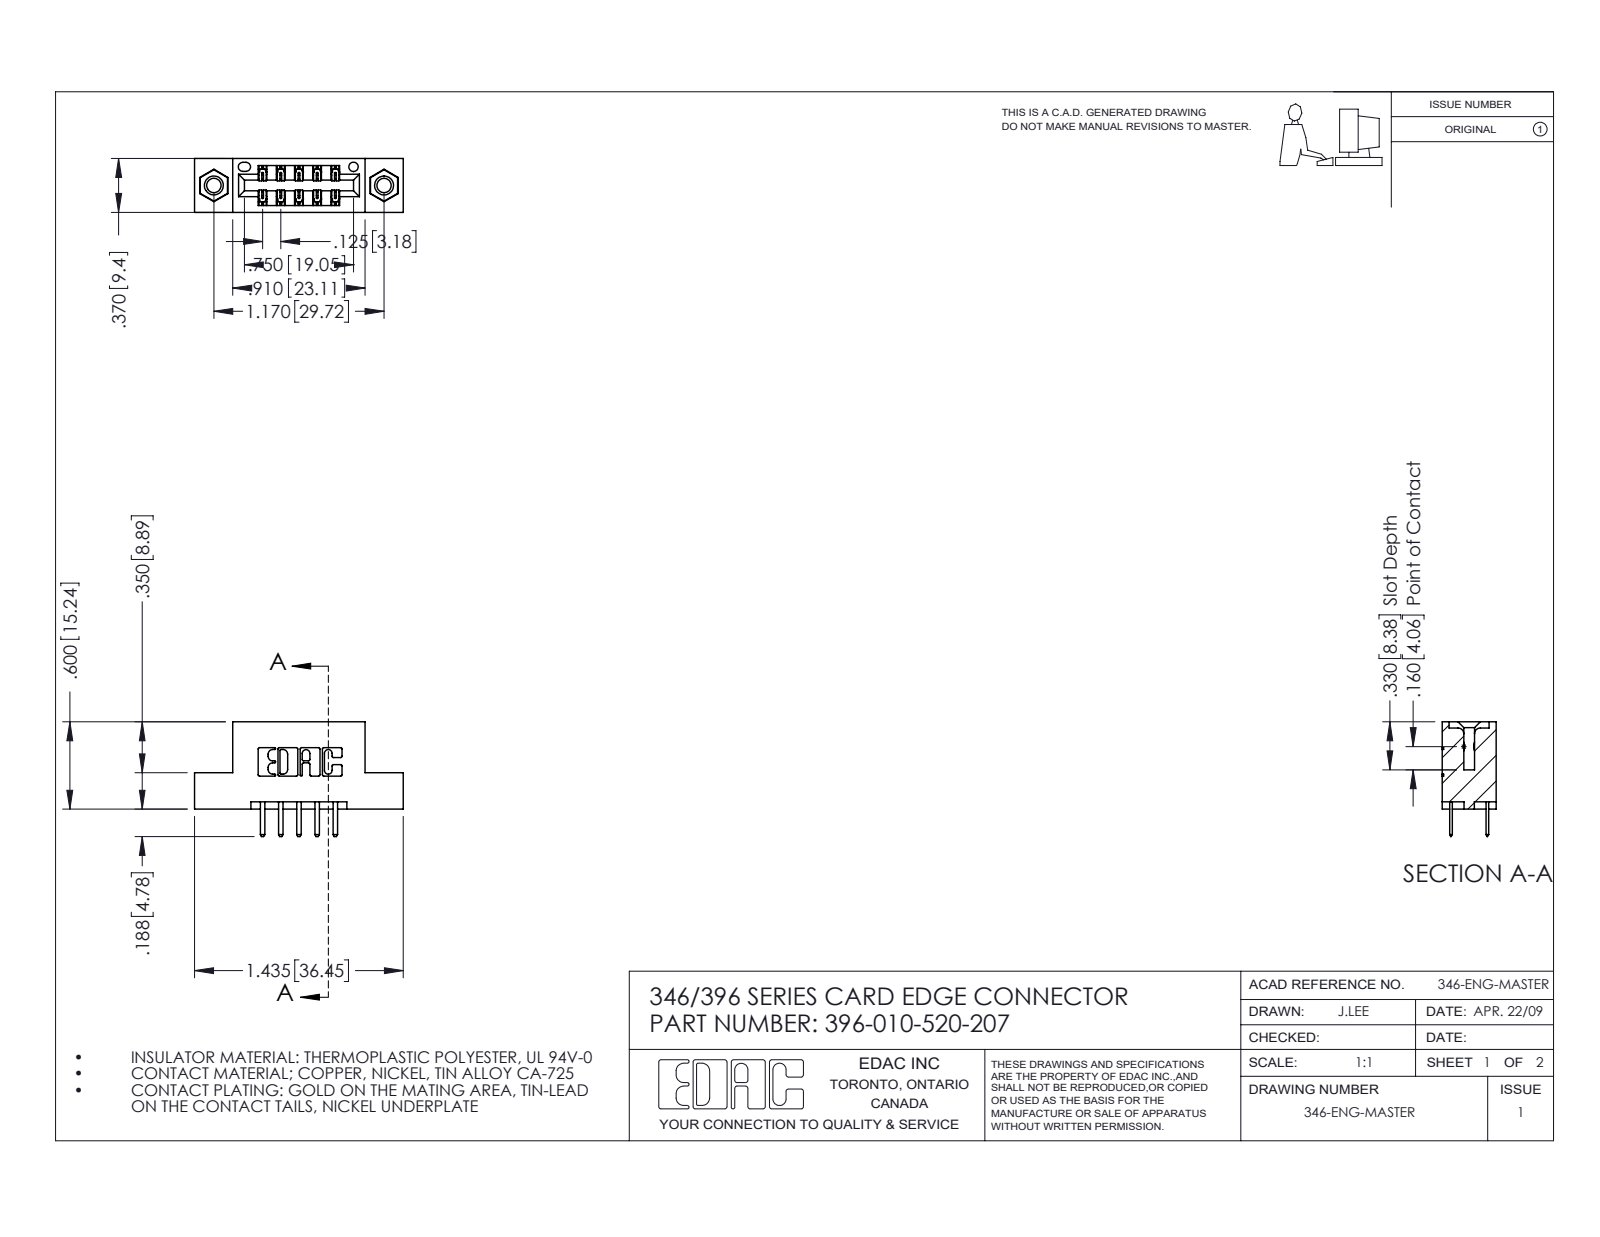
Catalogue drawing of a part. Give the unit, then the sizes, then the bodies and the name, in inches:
Units: inches
Overall size (bounding box): 1.435 × 0.788 × 0.37
Round holes (diameter × count): ⌀0.098 ×2, ⌀0.125 ×2, ⌀0.156 ×2, ⌀0.064 ×1
Round bosses / shafts (diameter × count): ⌀0.155 ×2
Partial cylindrical surfaces — rounded edges, fillets, slot ends (radius × count): R0.01 ×22, R0.006 ×15, R0.01 ×14, R0.007 ×6, R0.031 ×6, R0.026 ×3, R0.014 ×2, R0.022 ×2
Main face-to-face distances: 0.25, 0.37, 0.048, 0.322, 0.148, 0.222, 0.1, 0.174, 0.125, 0.55
Hole centre spacings: 0.246, 0.969, 1.17
Volume: 0.198 in³ · Surface area: 6.057 in²
Bodies: 13 solids, 742 faces (478 planar, 248 cylindrical, 16 other)
Part name (STEP PRODUCT): 346 Part_Flush Mounting Lugs - 0.156 Dia-TI; 345-250-001_345-250-005-103; 396-010-520-207; 345-292-001_345-293-120
STEP written by: SolidWorks 2016 (CONFIG_CONTROL_DESIGN)
